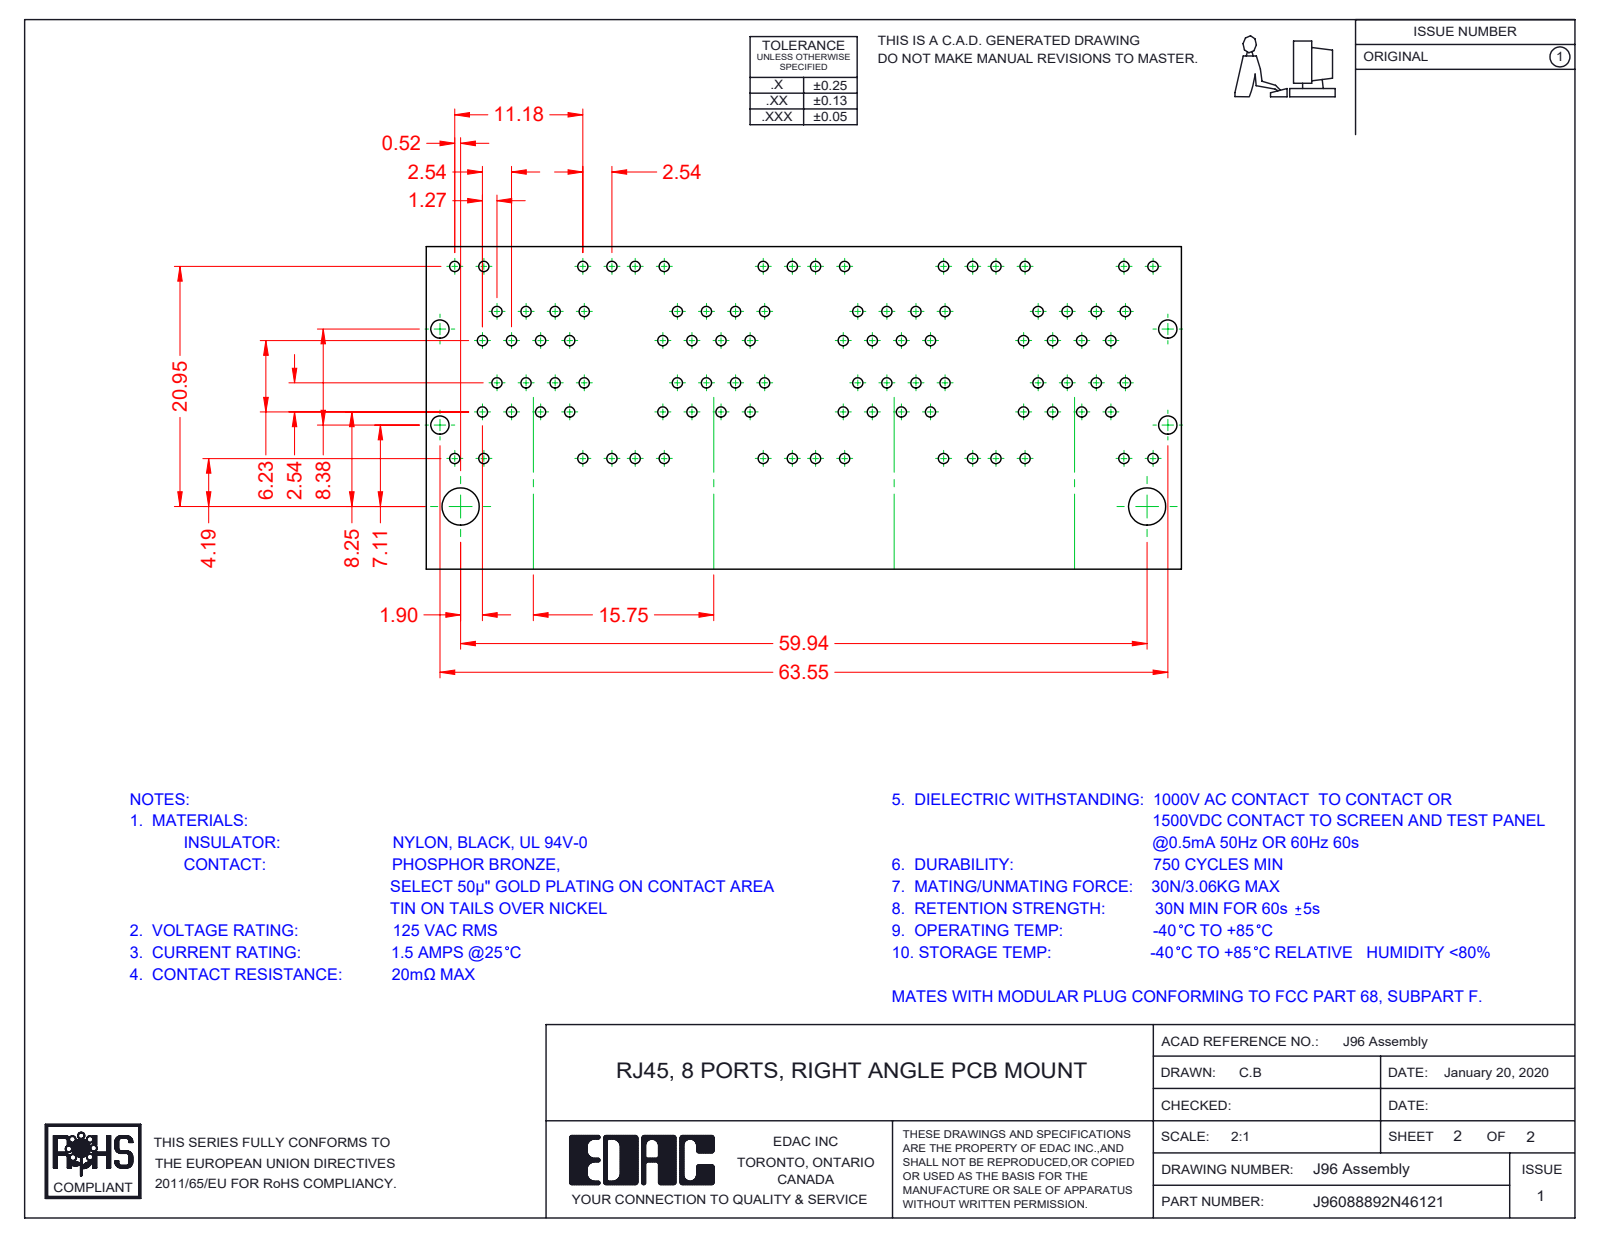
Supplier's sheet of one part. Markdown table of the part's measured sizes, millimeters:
| quantity | value |
| --- | --- |
| part name | 96 Contacts Upper; 96 Contact Lock Lower; 96 Grounding_8 Ports; 96 Contacts Lower (+8 more) |
| STEP written by | SolidWorks 2016 (CONFIG_CONTROL_DESIGN) |
| units | millimeters |
| bodies | 96 solids, 7658 faces (6069 planar, 1323 cylindrical, 266 other) |
| overall size | 64.05 × 29.58 × 28.68 |
| volume | 24 160 mm³ |
| surface area | 63 658 mm² |
| round holes (diameter × count) | 1.7 × 3 |
| round bosses / shafts (diameter × count) | 1.68 × 3 |
| partial cylindrical surfaces (radius × count) | 0.25 × 124, 0.35 × 73, 1 × 72, 0.5 × 49, 0.91 × 32, 0.2 × 21, 0.7 × 11, 0.22 × 8 |
| main face-to-face distances | 15.75, 0.35, 9.95, 1.17, 1.6, 0.54, 9.98, 10.18, 12.67, 3.37 |
| hole center spacings | 15.75, 31.5 |
